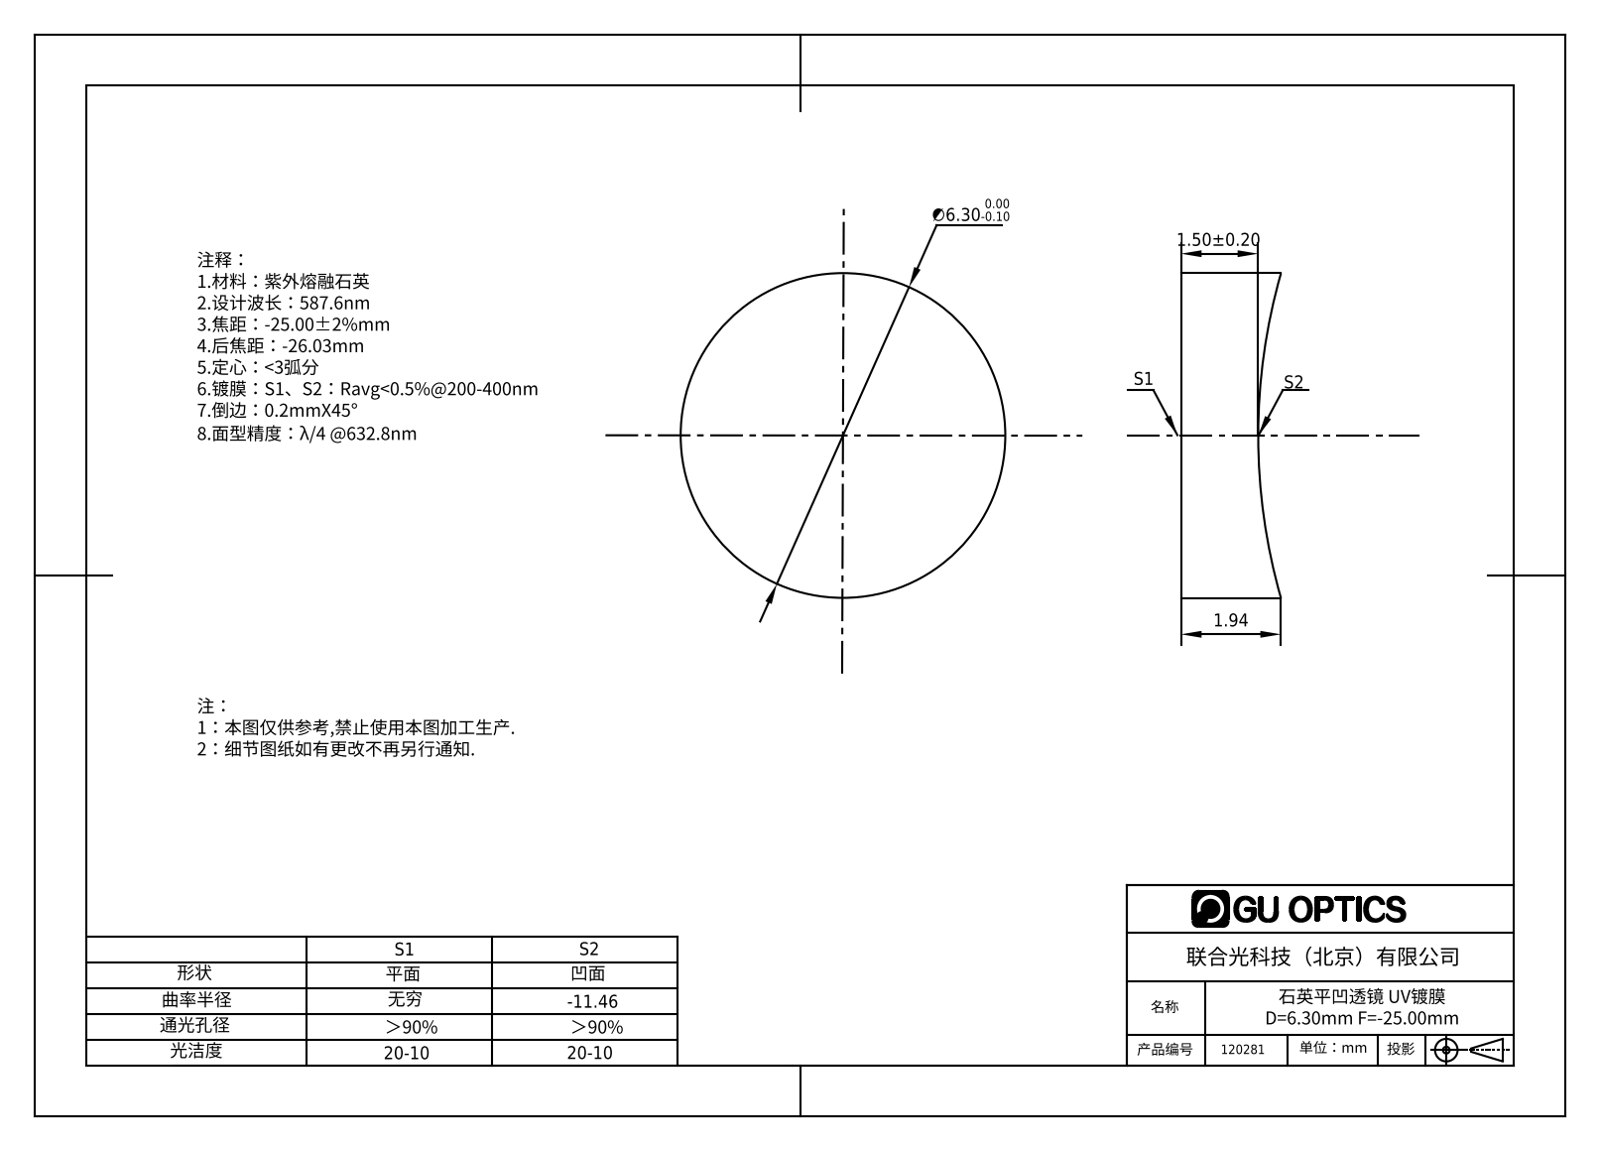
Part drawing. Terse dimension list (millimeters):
name: 120248
written by: SolidWorks 2016 (AUTOMOTIVE_DESIGN)
unit: mm
bodies: 1 solid, 5 faces (1 planar, 2 cylindrical, 2 other)
size: 6.3 × 6.3 × 1.94
volume: 54 mm³; area: 101 mm²
bosses: 1× ⌀6.3
